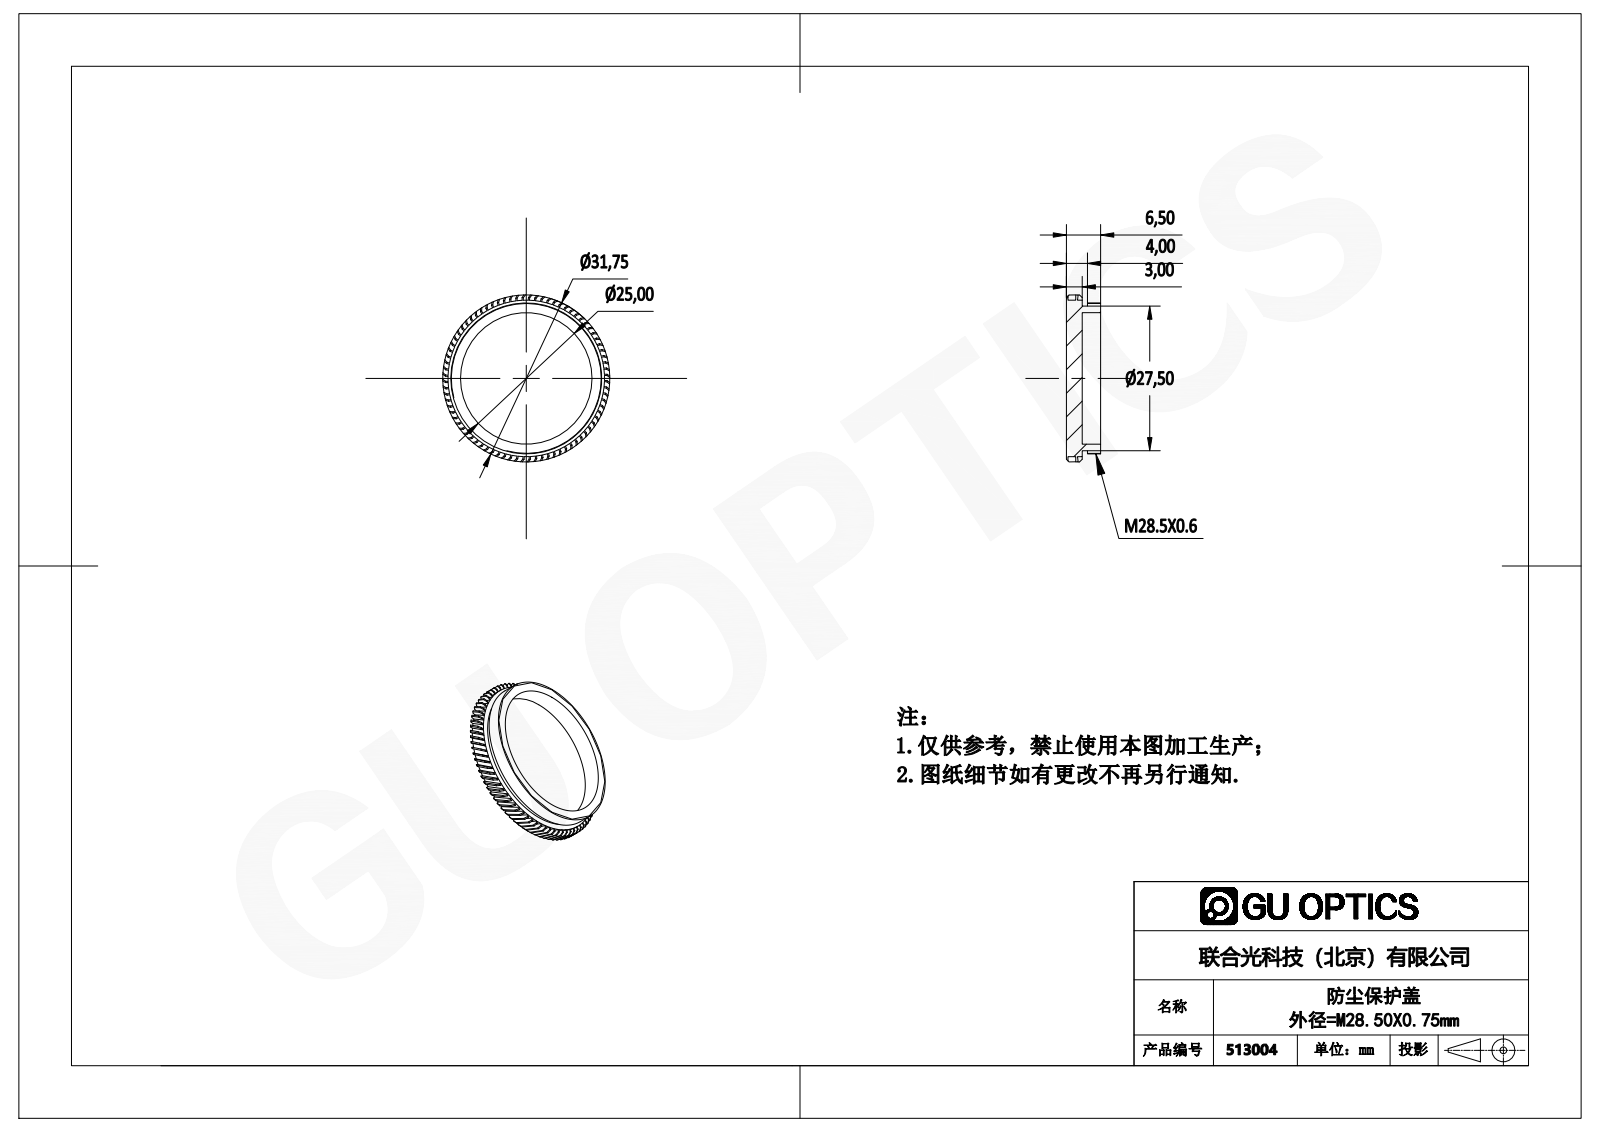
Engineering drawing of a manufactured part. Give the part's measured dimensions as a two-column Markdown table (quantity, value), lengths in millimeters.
| quantity | value |
| --- | --- |
| part name | 513004 |
| STEP written by | SolidWorks 2016 (AUTOMOTIVE_DESIGN) |
| units | millimeters |
| bodies | 1 solid, 573 faces (165 planar, 247 cylindrical, 161 other) |
| overall size | 31.75 × 31.75 × 6.5 |
| volume | 2 634 mm³ |
| surface area | 2 932 mm² |
| round holes (diameter × count) | 25 × 1 |
| round bosses / shafts (diameter × count) | 31.75 × 1, 29.75 × 1, 28.7 × 1, 27.5 × 1 |
| main face-to-face distances | 3, 0.8, 3.5, 6.5, 2.5, 1, 4 |
